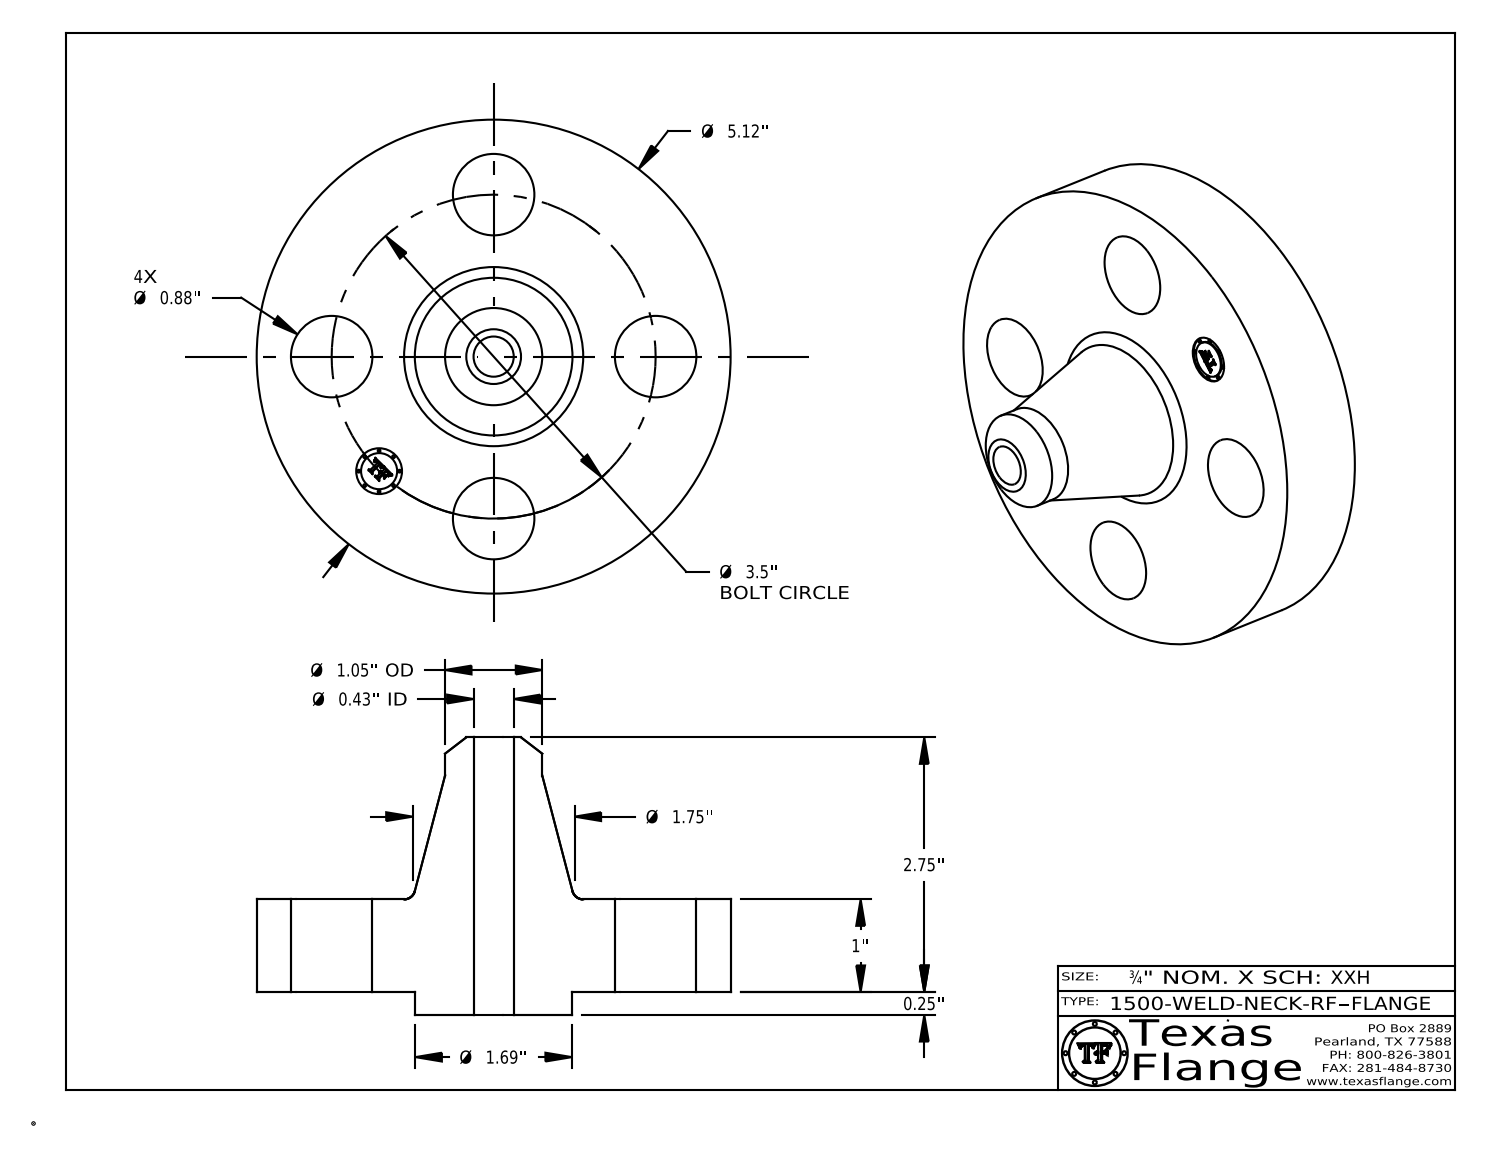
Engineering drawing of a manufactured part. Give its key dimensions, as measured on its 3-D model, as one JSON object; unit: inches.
{"part_name": "1500-WELD-NECK-RF", "step_written_by": "CATIA V5 STEP AP214 (AUTOMOTIVE_DESIGN)", "units": "inches", "bodies": {"solids": 1, "faces": 411, "planar": 369, "cylindrical": 36, "other": 6}, "overall_size": [5.12, 5.12, 3], "volume_in3": 20.68, "surface_area_in2": 74, "round_holes": [[0.88, 4], [0.434, 1], [0.495, 1]], "round_bosses_or_shafts": [[0.03, 8], [5.12, 1], [1.69, 1], [1.05, 1], [0.39, 1]], "face_to_face_distances": [1, 0.25, 1.25, 3, 2.75, 1.75, 0.015, 1.235, 0.985, 1.765], "hole_center_spacings": [1.75, 2.475, 1.339, 3.233, 3.5]}
